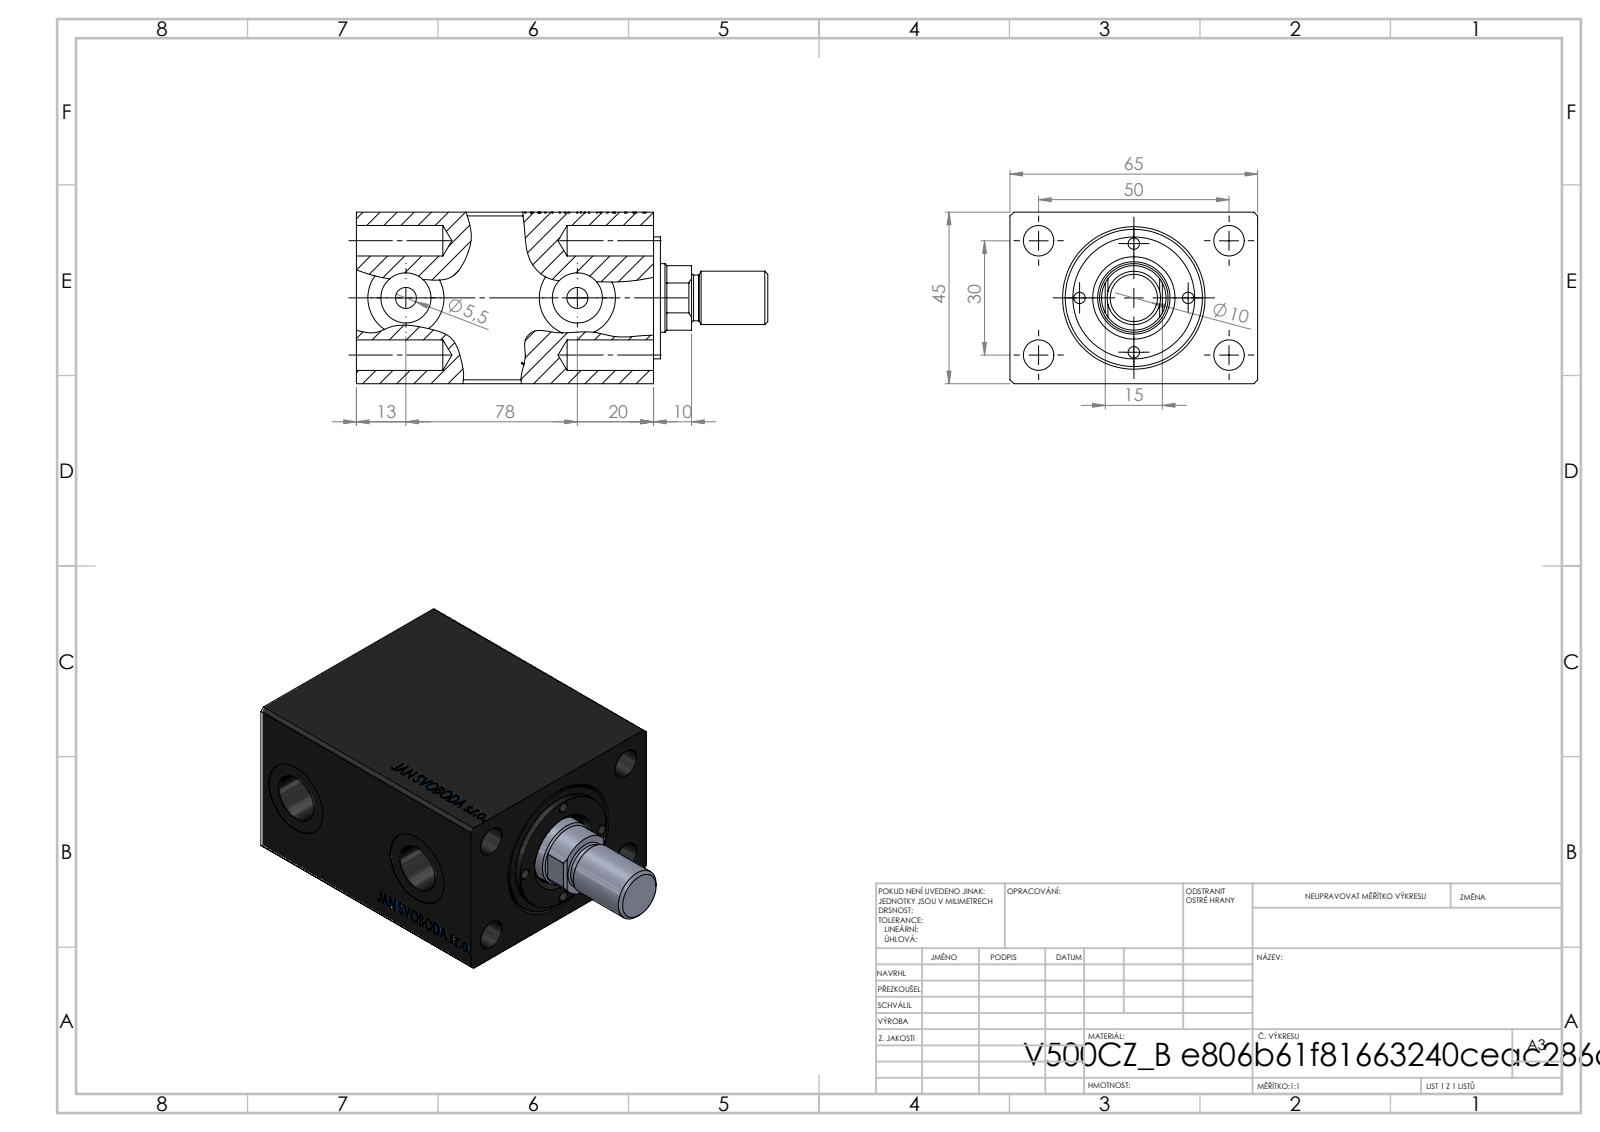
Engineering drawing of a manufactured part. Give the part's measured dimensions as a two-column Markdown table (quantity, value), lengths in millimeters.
| quantity | value |
| --- | --- |
| part name | V500CZ_vnitrni_cast_vysunovaci; V500CZ_FM; V500CZ |
| STEP written by | SolidWorks 2019 (CONFIG_CONTROL_DESIGN) |
| units | millimeters |
| bodies | 4 solids, 883 faces (402 planar, 63 cylindrical, 418 other) |
| overall size | 108 × 65 × 45 |
| volume | 213 895 mm³ |
| surface area | 44 126 mm² |
| round holes (diameter × count) | 3 × 4, 8 × 4, 5.5 × 2, 13.16 × 2, 20 × 2, 10 × 1, 18 × 1, 19 × 1, 25 × 1, 36 × 1 |
| round bosses / shafts (diameter × count) | 32 × 1, 14 × 1, 12 × 1 |
| partial cylindrical surfaces (radius × count) | 8.46 × 1 |
| main face-to-face distances | 45, 65, 78, 10, 68, 77.8, 67.8, 55, 22.8, 23 |
| hole center spacings | 14.25, 18.45, 20.15, 25.01, 29.15, 38.48, 42.02, 28.5 |
